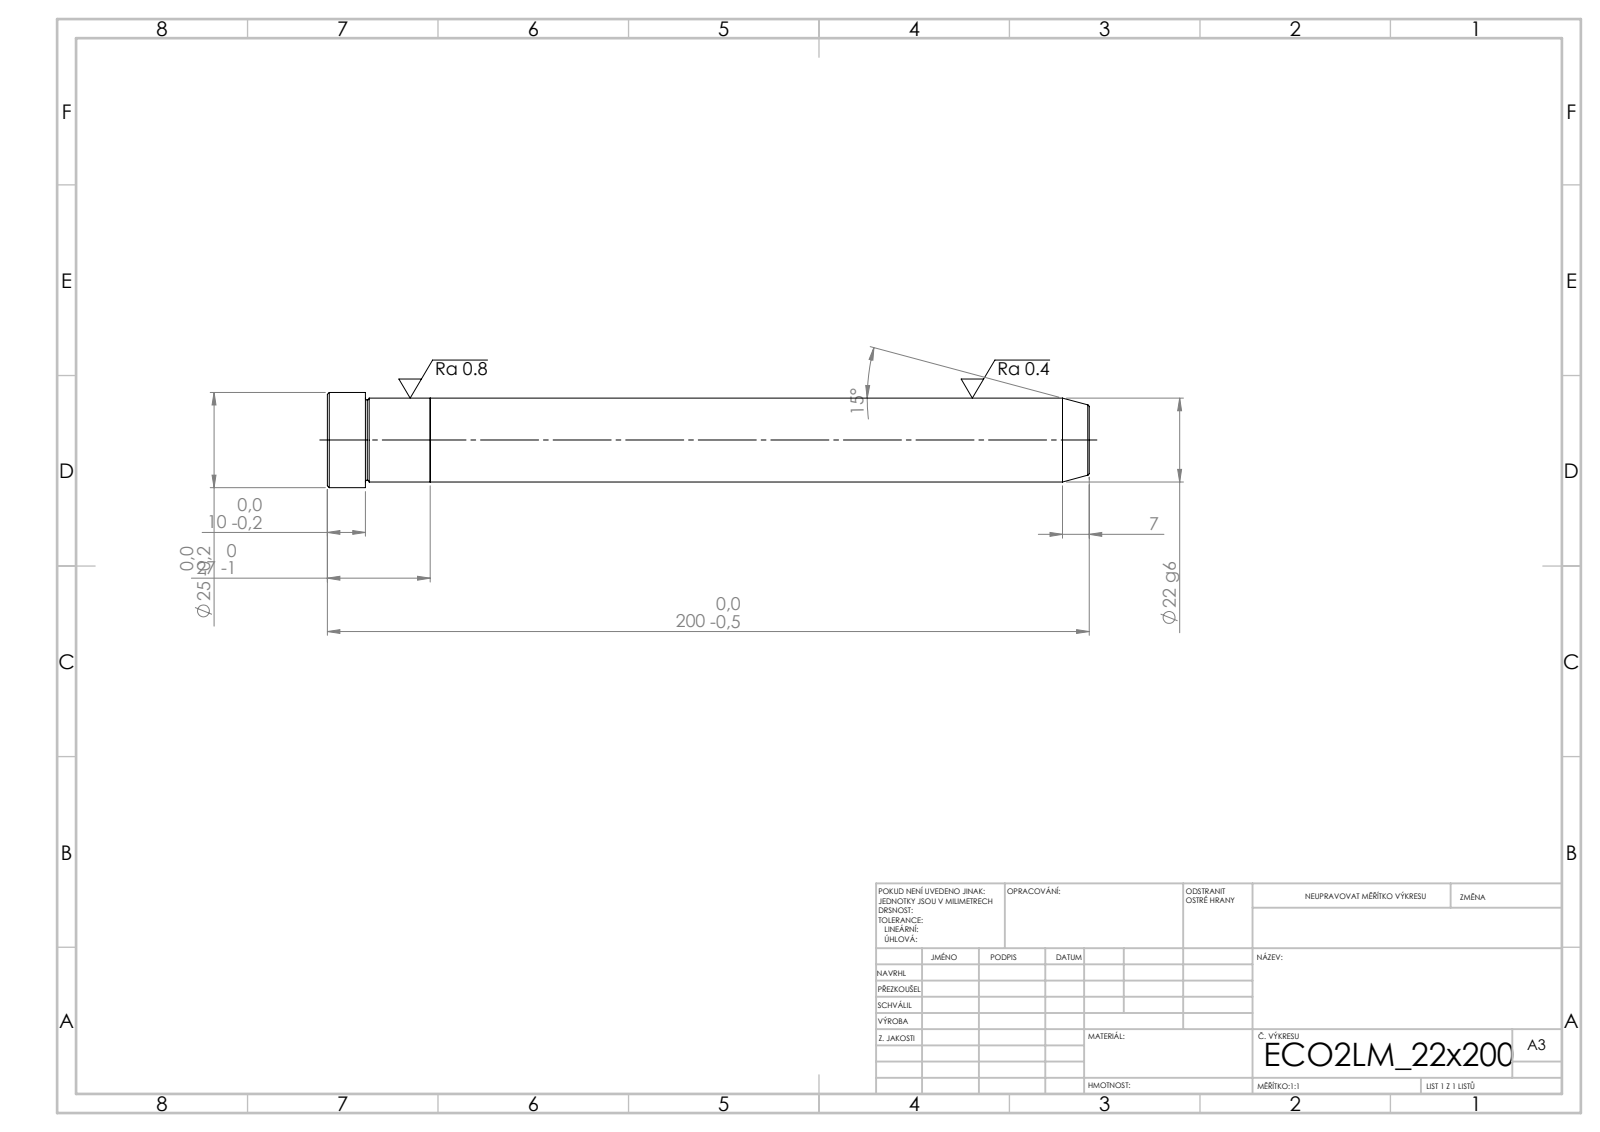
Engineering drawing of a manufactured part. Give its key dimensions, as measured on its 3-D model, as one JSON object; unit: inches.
{"step_written_by": "SolidWorks 2019 (CONFIG_CONTROL_DESIGN)", "units": "inches", "bodies": {"solids": 2, "faces": 21, "planar": 5, "cylindrical": 6, "other": 10}, "overall_size": [7.874, 0.984, 0.984], "volume_in3": 4.679, "surface_area_in2": 24.06, "round_bosses_or_shafts": [[0.984, 1], [0.866, 1]], "face_to_face_distances": [1.063, 6.811, 7.874, 7.48, 0.669, 0.394]}
